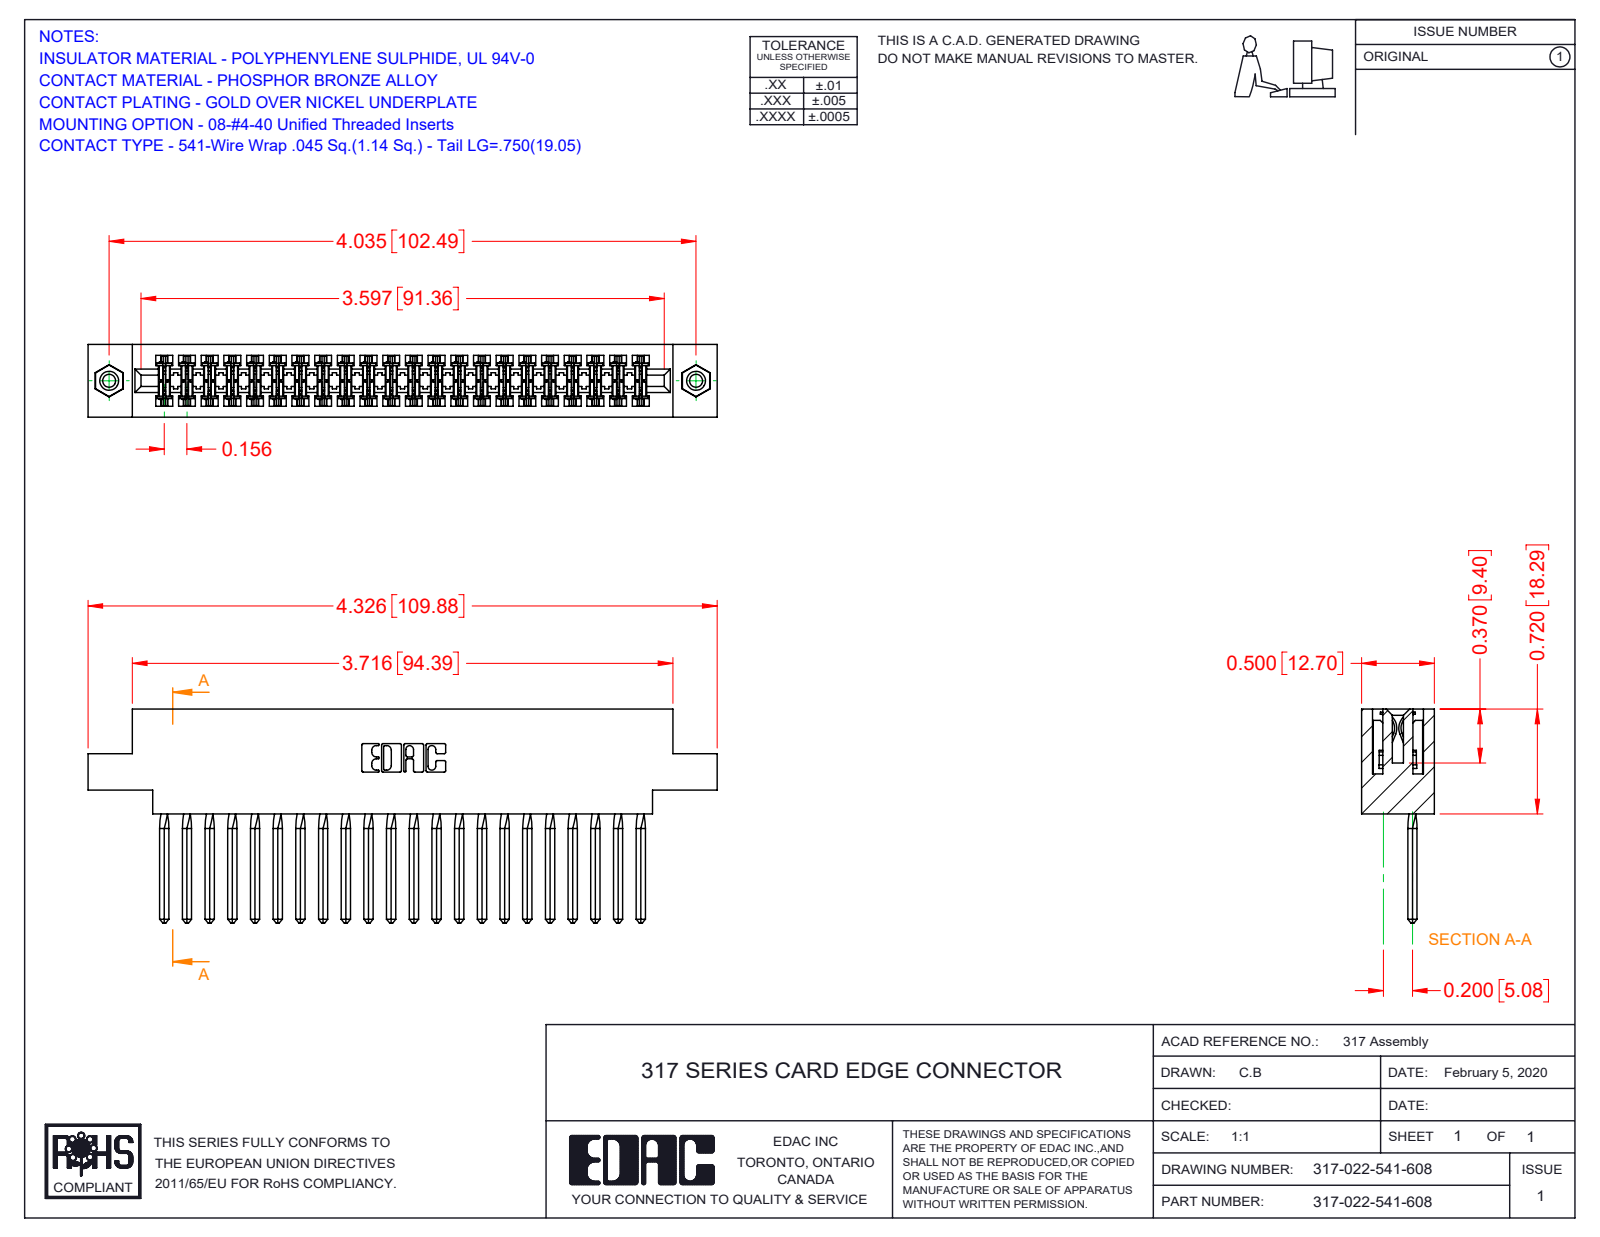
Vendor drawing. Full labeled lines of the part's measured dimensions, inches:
Part name (STEP PRODUCT): 317 Part_.156 Dia - TI; 317-290-002_541; 317-022-541-608; 345-250-001_345-250-003-102
STEP written by: SolidWorks 2016 (CONFIG_CONTROL_DESIGN)
Units: inches
Bodies: 25 solids, 3506 faces (2818 planar, 584 cylindrical, 104 other)
Overall size (bounding box): 4.326 × 1.47 × 0.5
Volume: 1.049 in³ · Surface area: 36.67 in²
Round holes (diameter × count): ⌀0.089 ×2, ⌀0.125 ×2, ⌀0.156 ×2
Round bosses / shafts (diameter × count): ⌀0.155 ×2
Partial cylindrical surfaces — rounded edges, fillets, slot ends (radius × count): R0.015 ×44, R0.01 ×22, R0.007 ×6, R0.031 ×6, R0.026 ×3, R0.095 ×2, R0.1 ×2, R0.11 ×2
Main face-to-face distances: 0.5, 0.075, 0.425, 0.11, 0.35, 0.195, 0.772, 0.22, 0.662, 0.72
Hole centre spacings: 4.035
